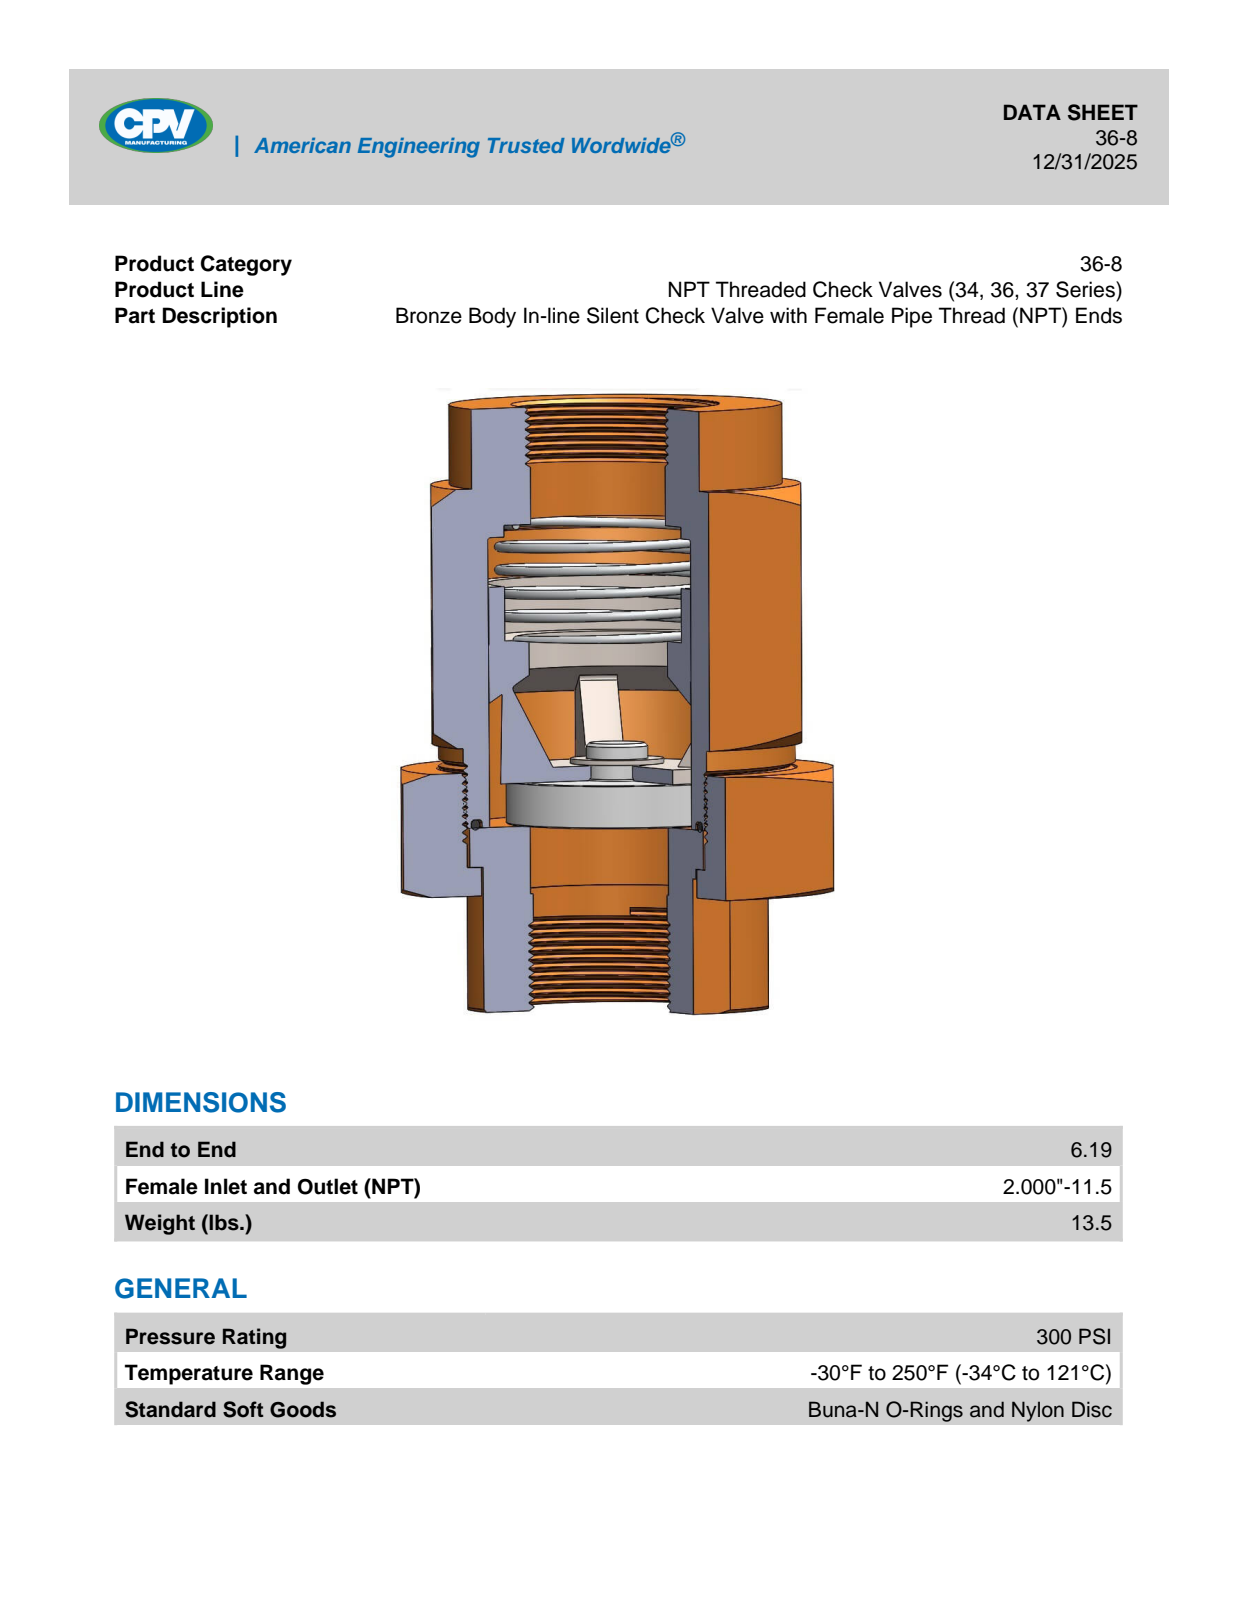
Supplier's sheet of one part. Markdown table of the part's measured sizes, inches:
| quantity | value |
| --- | --- |
| part name | 36-8 |
| STEP written by | SolidWorks 2018 (AUTOMOTIVE_DESIGN) |
| units | inches |
| bodies | 1 solid, 120 faces (29 planar, 47 cylindrical, 44 other) |
| overall size | 6.125 × 5.058 × 4.38 |
| volume | 63.77 in³ |
| surface area | 134.1 in² |
| round holes (diameter × count) | 2 × 1 |
| round bosses / shafts (diameter × count) | 3.62 × 1, 3.38 × 1 |
| partial cylindrical surfaces (radius × count) | 1.585 × 1 |
| main face-to-face distances | 3.75, 0.315, 4.065, 4.38, 0.315, 4.065, 4.94, 1.25, 3.69, 1.185 |
